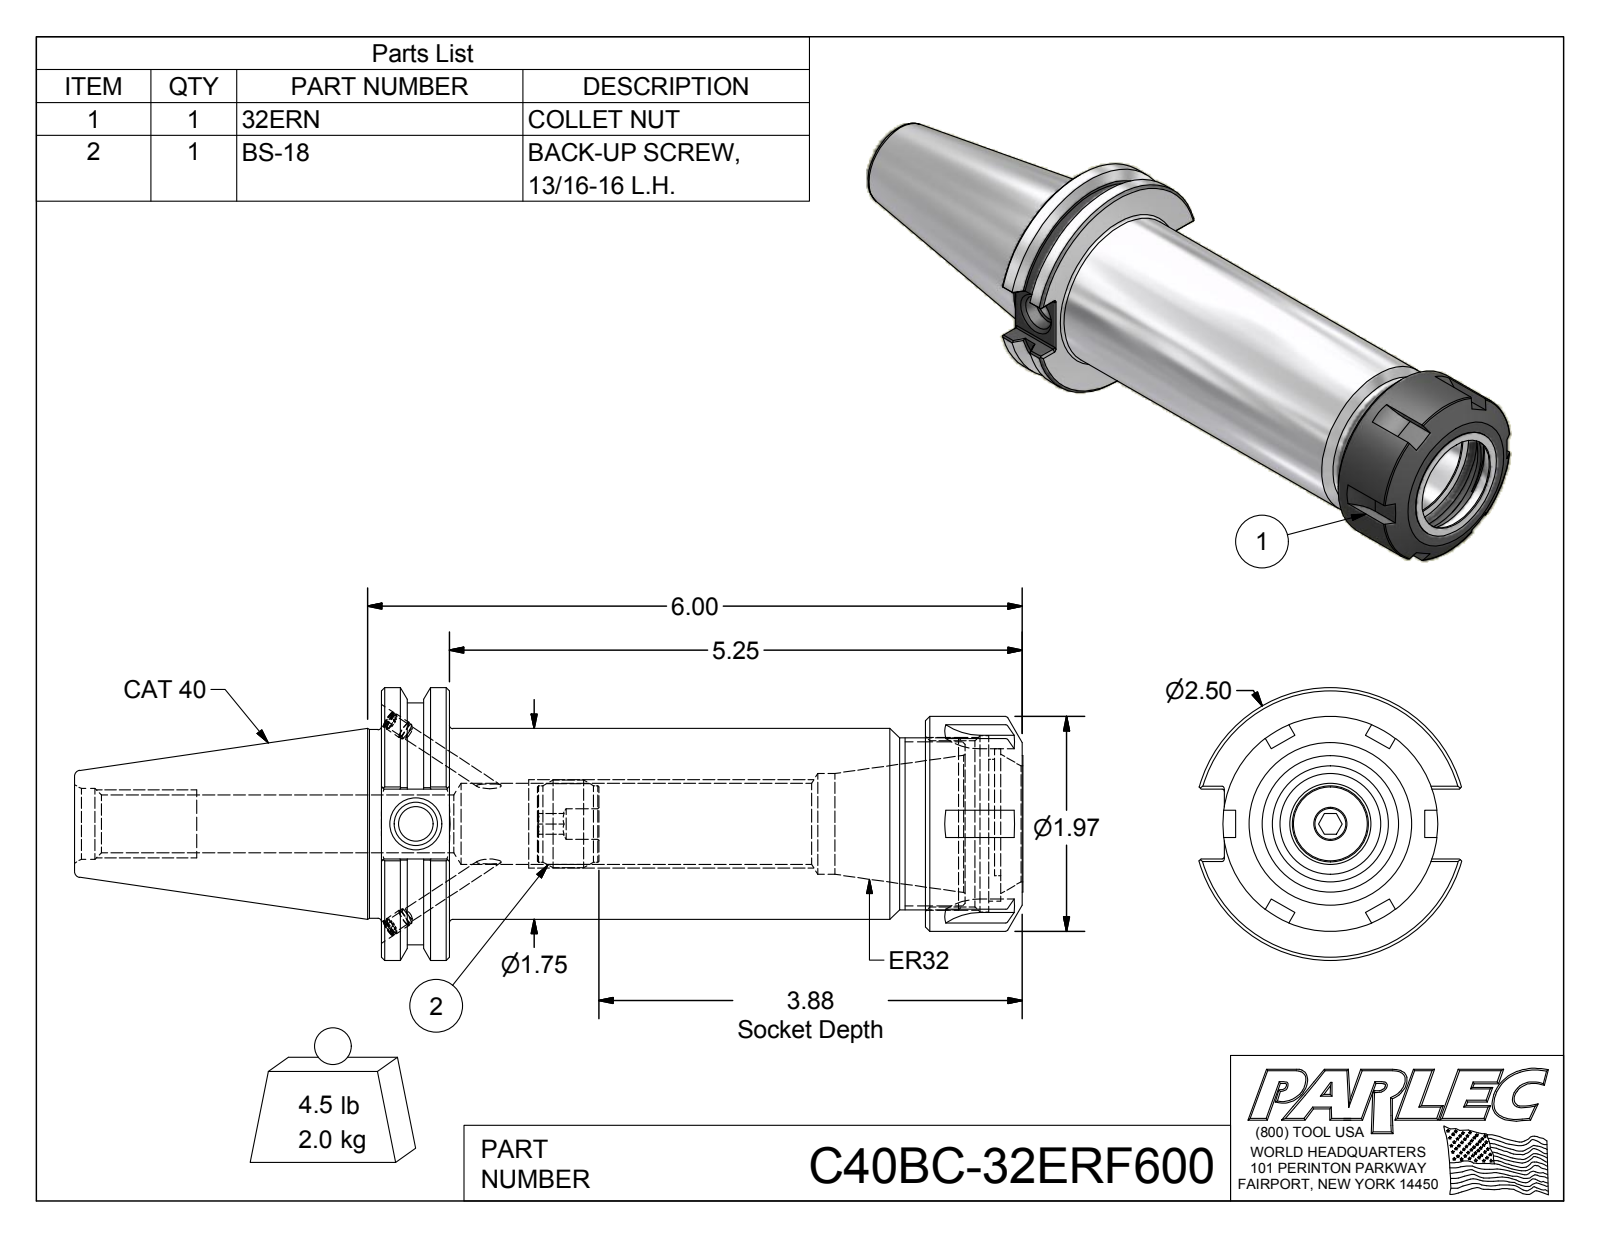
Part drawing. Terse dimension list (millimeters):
name: C40BCB-32ER6-1; 029-965; 32ERN; BS-18 (+1 more)
written by: Autodesk Inventor 2016 (AUTOMOTIVE_DESIGN)
unit: mm
bodies: 5 solids, 229 faces (96 planar, 60 cylindrical, 73 other)
size: 220.65 × 63.5 × 61.11
volume: 258 970 mm³; area: 55 306 mm²
holes: 2× ⌀3.3, 2× ⌀4.1, 1× ⌀7.11, 1× ⌀8, 1× ⌀10.13, 1× ⌀13.39, 1× ⌀16.46, 1× ⌀18.92, 1× ⌀23.5, 1× ⌀27, 1× ⌀33.02, 1× ⌀38.65
bosses: 2× ⌀4.2, 2× ⌀4, 1× ⌀63.5, 1× ⌀56.36, 1× ⌀50, 1× ⌀44.45, 1× ⌀43.94, 1× ⌀40
rounds: 24× R0.51, 1× R14.9, 1× R17.5
face distances: 15.88, 149.23, 133.35, 126.45, 110.57, 22.78, 141.46, 125.58, 15.01, 7.77
hole spacings: 1.85
